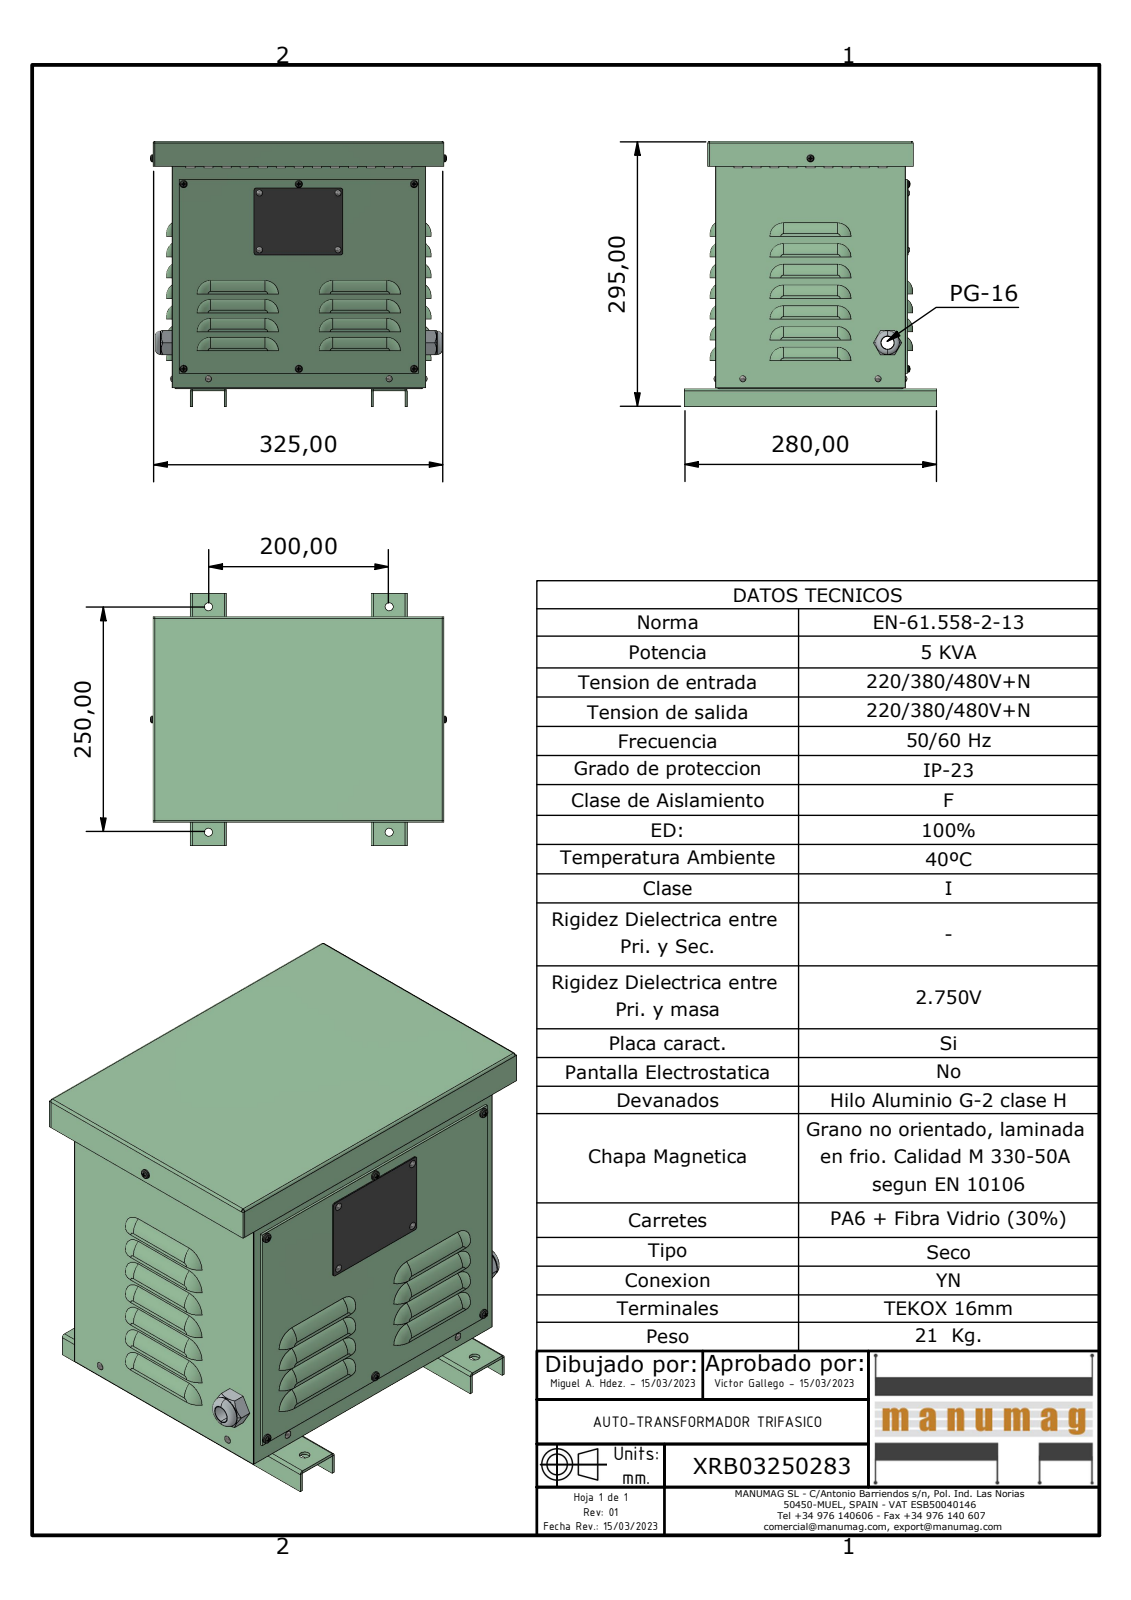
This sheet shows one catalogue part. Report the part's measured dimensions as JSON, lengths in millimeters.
{"part_name": "XRB03250283; JE003 - JE004 - JE005 EXPORT BASE; JE003 - JE004 - JE005 EXPORT PATA; JE003 - JE004 - JE005 EXPORT CUERPO (+6 more)", "step_written_by": "Autodesk Inventor 2023 (AUTOMOTIVE_DESIGN)", "units": "millimeters", "bodies": {"solids": 29, "faces": 1436, "planar": 841, "cylindrical": 283, "other": 312}, "overall_size": [328.13, 294.5, 280], "volume_mm3": 827636, "surface_area_mm2": 1061000, "round_holes": [[4.8, 13], [3, 12], [9, 6], [3.8, 5], [4, 4], [14, 1], [24, 1]], "round_bosses_or_shafts": [[3.2, 8], [4, 7], [3.62, 7], [26, 1], [23, 1], [22.5, 1]], "partial_cylinders_radius": [[14, 44], [4, 25], [15, 25], [0.5, 9], [2, 8], [4.5, 8], [1.5, 6], [1.5, 4]], "face_to_face_distances": [0.5, 2, 210.5, 280.5, 2.5, 1.5, 274.5, 272.5, 211, 213], "hole_center_spacings": [127.5, 200, 241.42, 205, 29.62, 44.63, 47, 63]}
